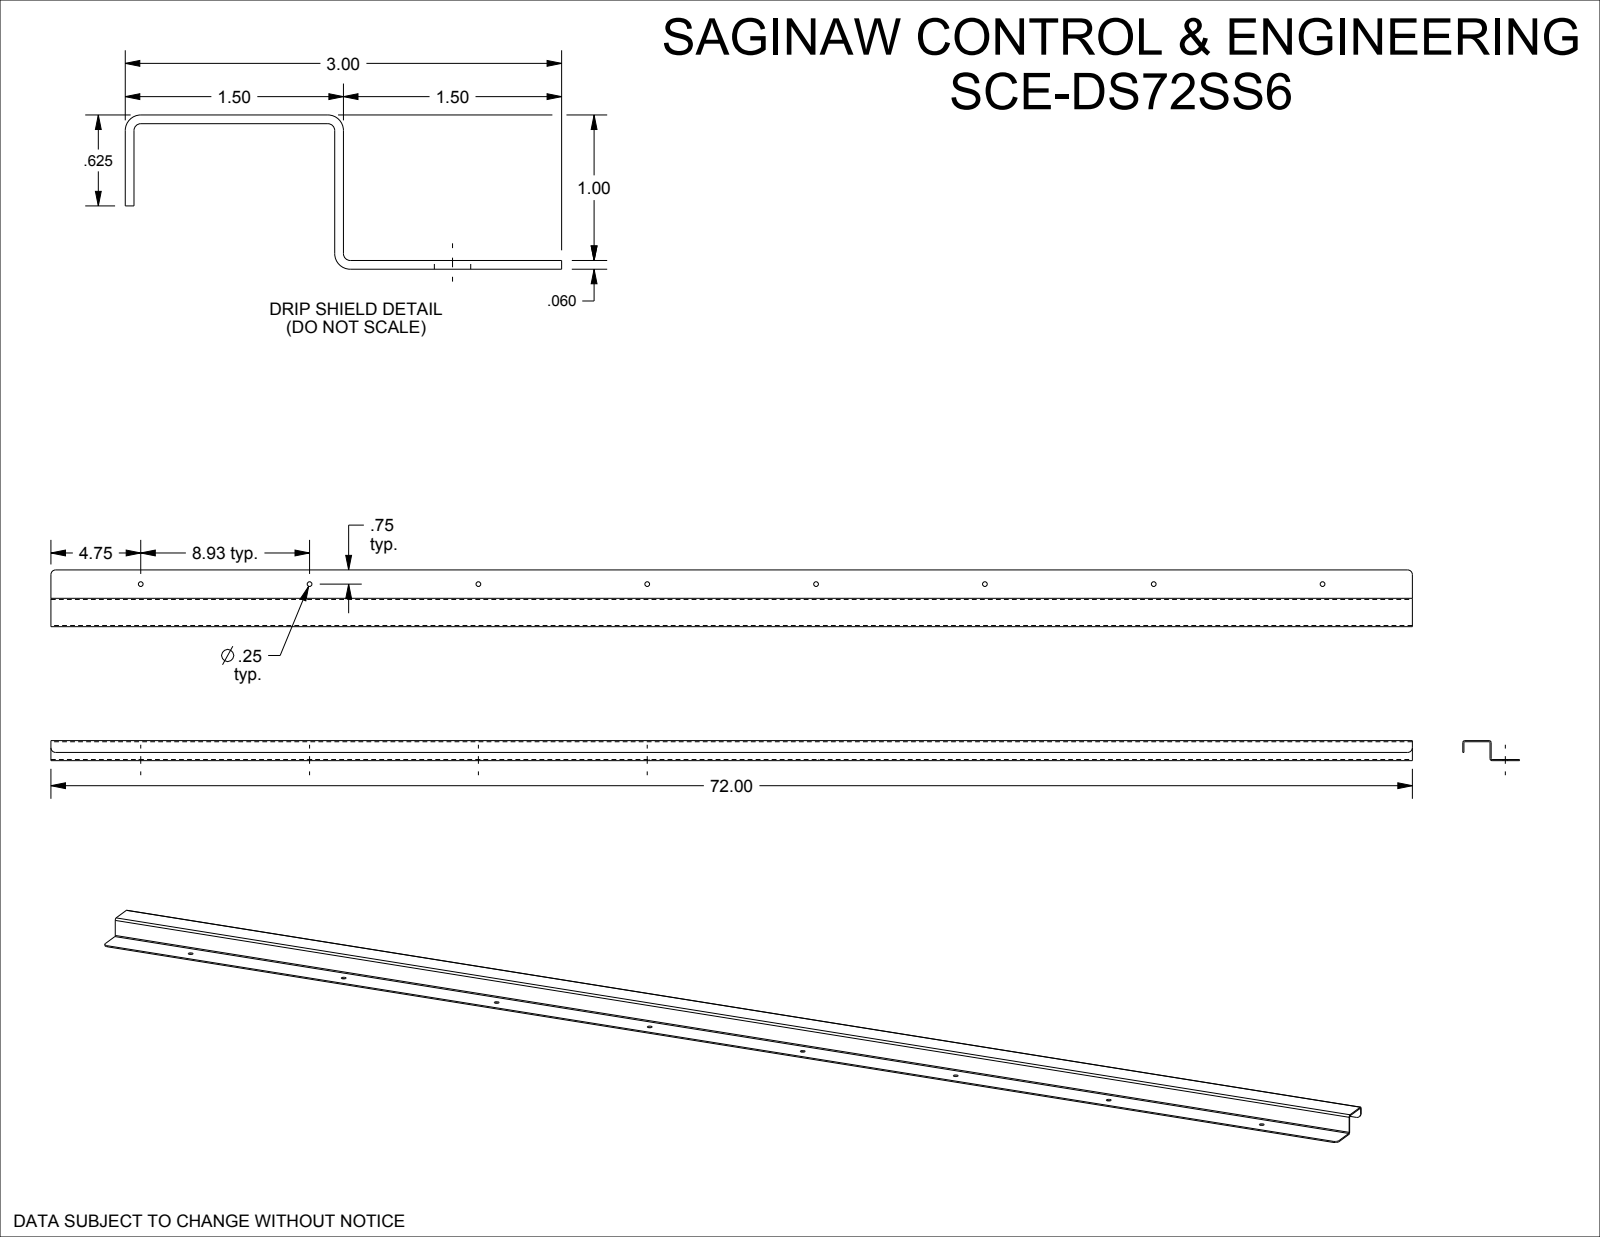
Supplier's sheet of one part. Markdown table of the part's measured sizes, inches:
| quantity | value |
| --- | --- |
| part name | SCE-DS72SS6 |
| STEP written by | SolidWorks 2019 (CONFIG_CONTROL_DESIGN) |
| units | inches |
| bodies | 1 solid, 30 faces (12 planar, 18 cylindrical, 0 other) |
| overall size | 72 × 3 × 1.06 |
| volume | 19.27 in³ |
| surface area | 651.7 in² |
| round holes (diameter × count) | 0.25 × 8 |
| partial cylindrical surfaces (radius × count) | 0.25 × 4, 0.047 × 3, 0.107 × 3 |
| main face-to-face distances | 0.06, 1, 0.94, 1.06, 1.44, 1.5, 1.38, 0.435, 0.375, 0.565 |
| hole center spacings | 17.857, 8.929, 35.714, 8.928, 26.786, 26.785, 44.643, 53.571 |
